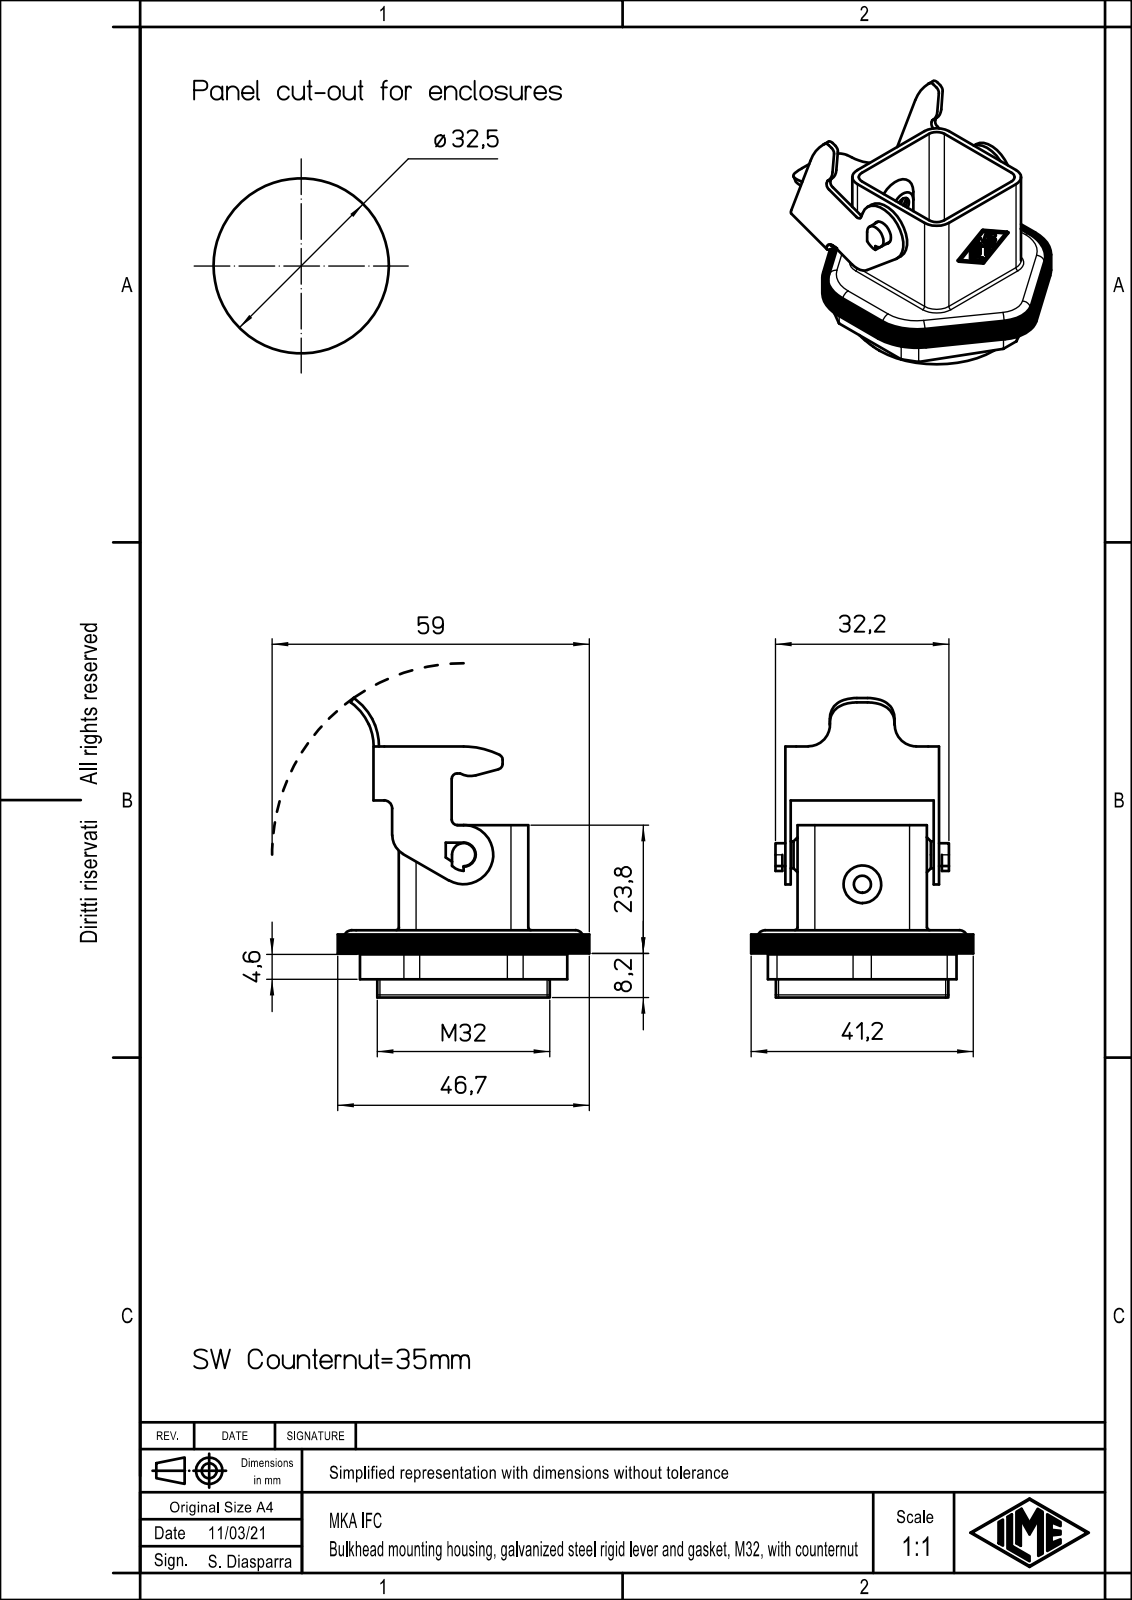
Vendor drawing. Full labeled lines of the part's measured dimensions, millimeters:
Part name (STEP PRODUCT): MKA_IFC; Counternut
STEP written by: Creo Elements/Direct Modeling 20.1B 02-Apr-2019 (C) Parametric Technology GmbH (AUTOMOTIVE_DESIGN)
Units: millimetres
Bodies: 2 solids, 233 faces (122 planar, 94 cylindrical, 17 other)
Overall size (bounding box): 57.66 × 41.2 × 39.4
Volume: 11 879 mm³ · Surface area: 12 370 mm²
Round holes (diameter × count): ⌀3.2 ×1, ⌀7 ×1
Round bosses / shafts (diameter × count): ⌀32 ×1, ⌀5 ×1, ⌀4.3 ×1
Partial cylindrical surfaces — rounded edges, fillets, slot ends (radius × count): R0.25 ×15, R1.5 ×7, R1 ×6, R2 ×6, R3.2 ×4, R4 ×4, R9.1 ×4, R10.1 ×4
Main face-to-face distances: 1.39, 22.61, 21.22, 24, 3.64, 24.86, 1, 27.5, 2.64, 23.86
